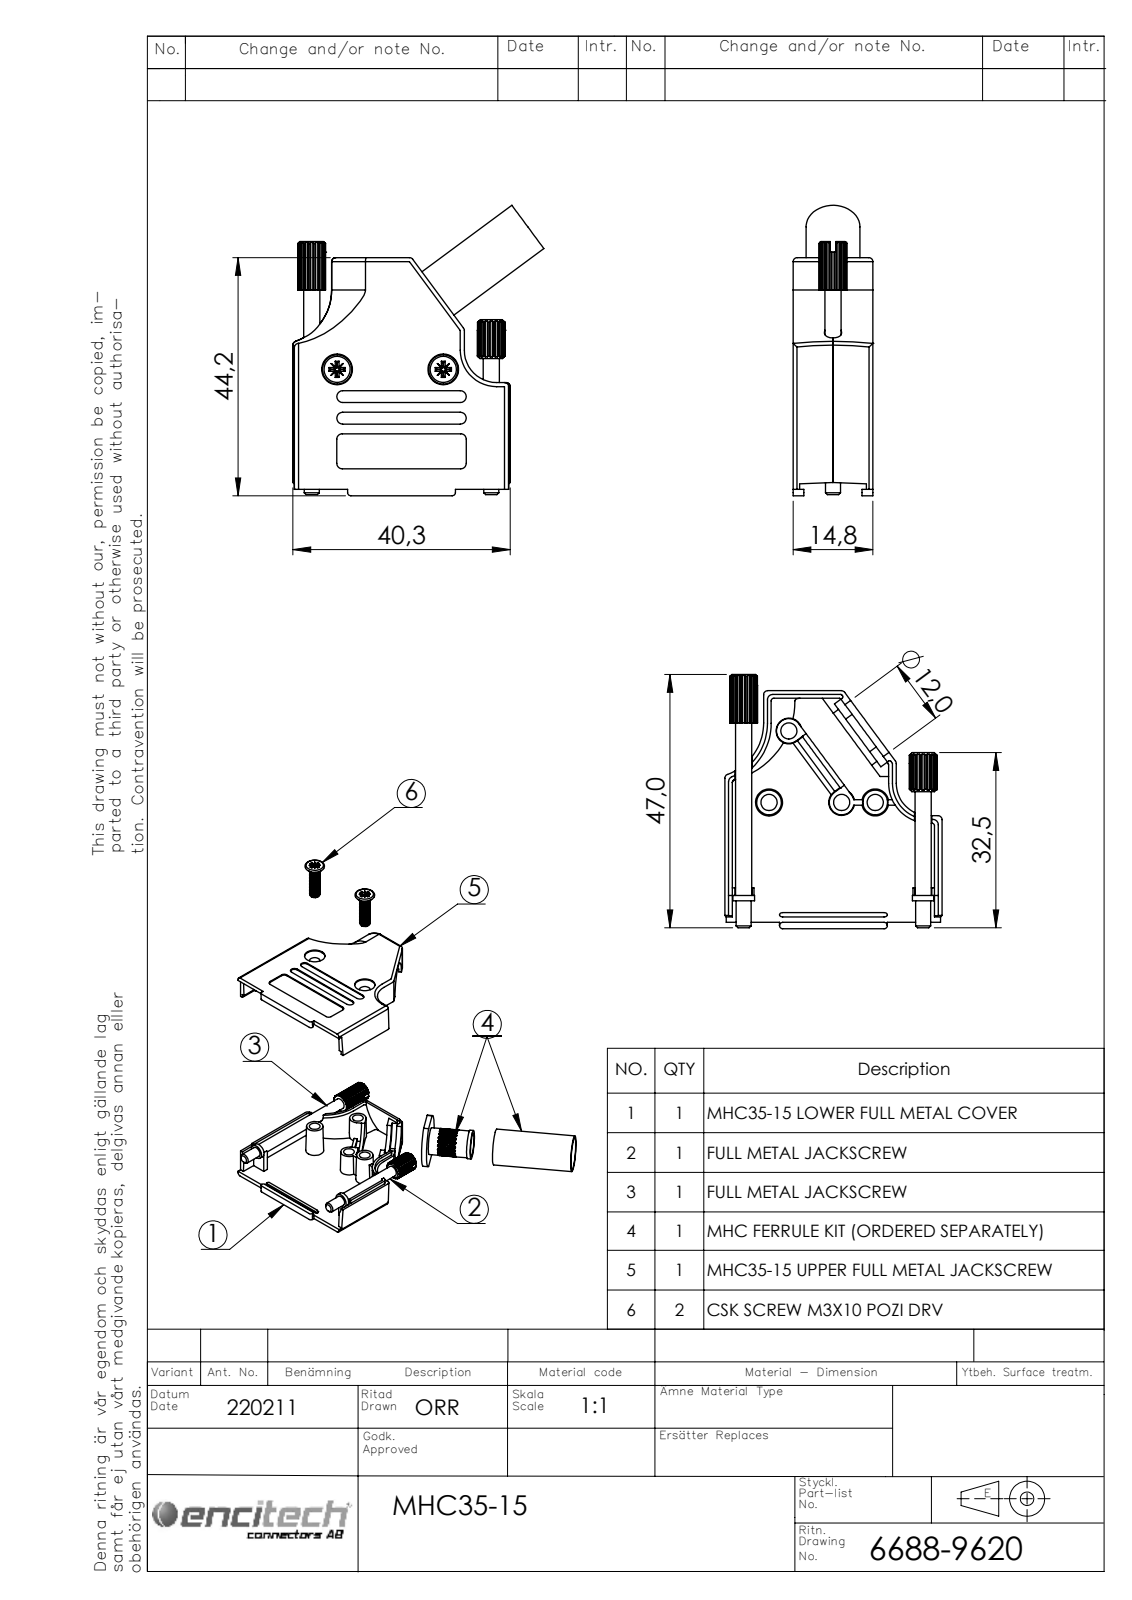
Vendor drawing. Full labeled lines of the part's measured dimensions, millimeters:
Part name (STEP PRODUCT): 6805-0139-02; 6522-0110-12; 6805-0139-12; 6855-0117-03 (+4 more)
STEP written by: SolidWorks 2021 (AUTOMOTIVE_DESIGN)
Units: millimetres
Bodies: 8 solids, 1707 faces (389 planar, 427 cylindrical, 891 other)
Overall size (bounding box): 53.91 × 46.56 × 14.8
Volume: 7 091 mm³ · Surface area: 13 461 mm²
Round holes (diameter × count): ⌀3 ×4, ⌀3.2 ×2, ⌀4.8 ×2, ⌀5.7 ×2, ⌀6.5 ×1, ⌀8.8 ×1, ⌀12 ×1
Round bosses / shafts (diameter × count): ⌀4 ×2, ⌀3 ×2, ⌀2.9 ×2, ⌀2.8 ×2, ⌀10 ×1, ⌀8 ×1, ⌀7.5 ×1
Partial cylindrical surfaces — rounded edges, fillets, slot ends (radius × count): R0.75 ×16, R0.1 ×8, R1 ×7, R0.3 ×5, R1.1 ×4, R0.38 ×3, R0.5 ×3, R0.6 ×2
Main face-to-face distances: 1.2, 13.6, 12.4, 14.8, 13.3, 14.5, 0.9, 6.2, 7.1, 7.4
Hole centre spacings: 6.23, 13.47, 13.77, 16.5, 19.7, 20.81, 33.3
